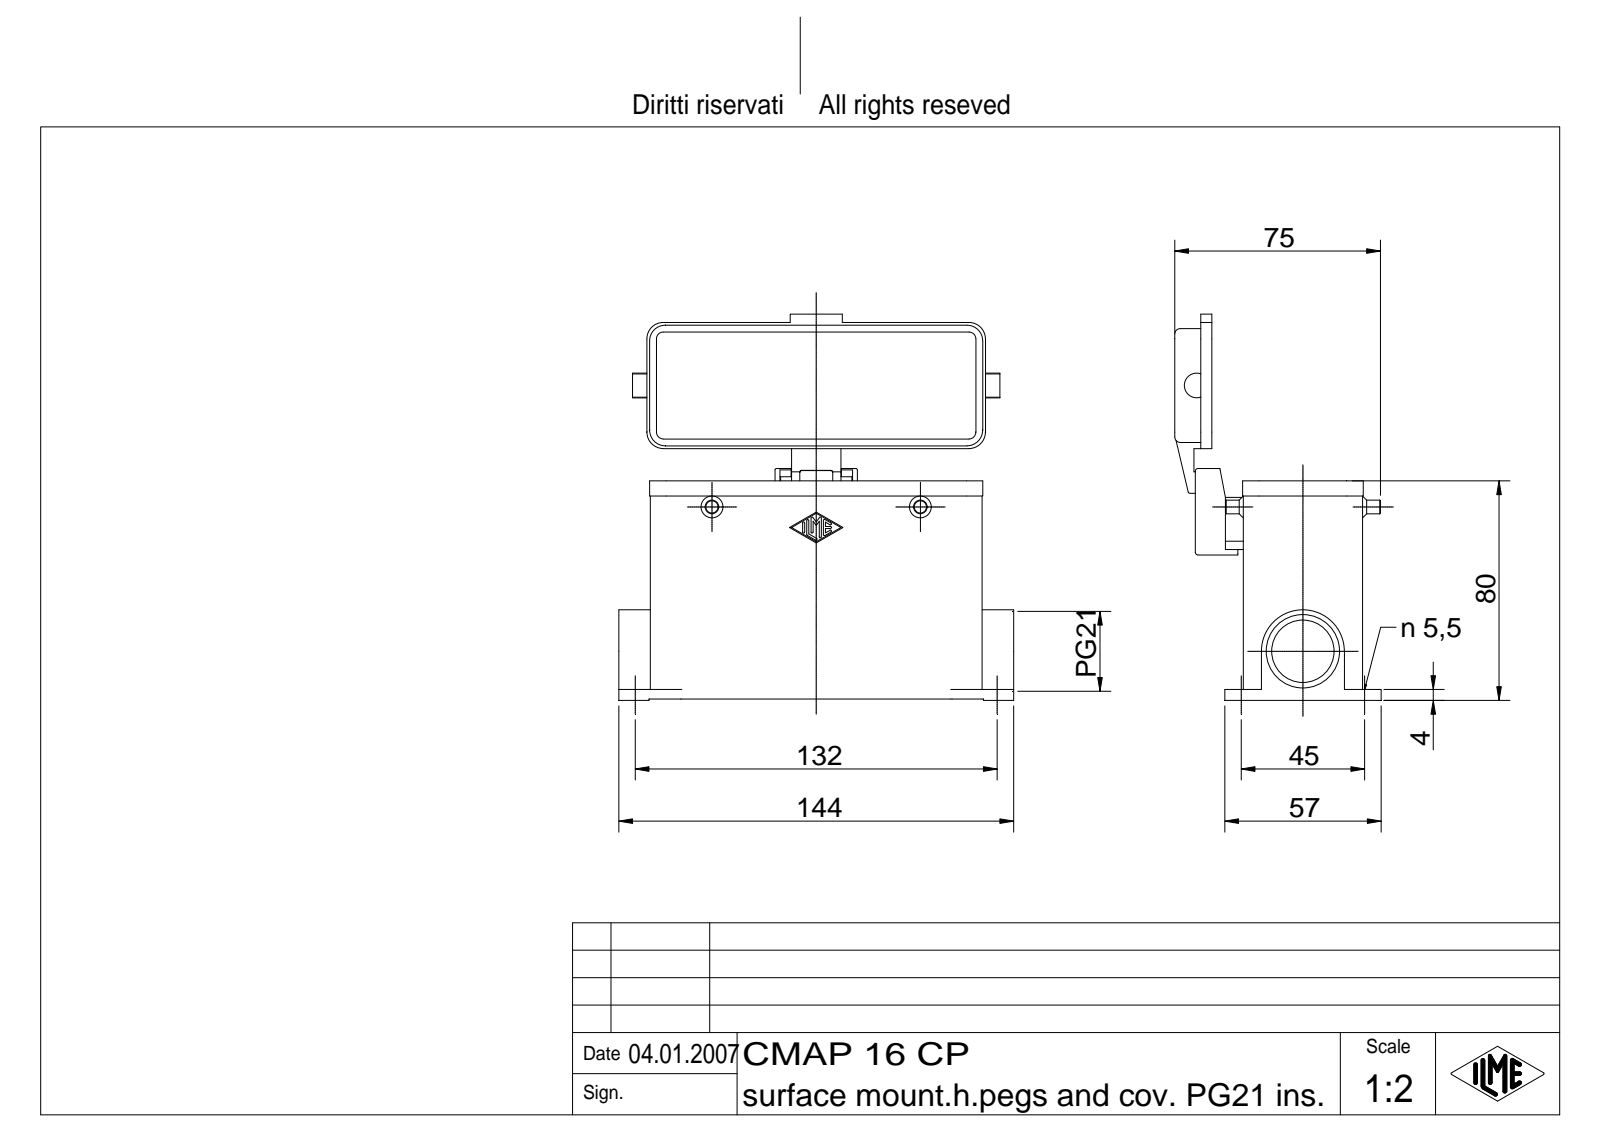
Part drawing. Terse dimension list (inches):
name: CMAP 16 CP
written by: Autodesk Inventor 7 (AUTOMOTIVE_DESIGN)
unit: in
bodies: 1 solid, 470 faces (195 planar, 164 cylindrical, 111 other)
size: 5.669 × 5.541 × 2.963
volume: 9.396 in³; area: 140.6 in²
holes: 4× ⌀0.217, 1× ⌀0.157, 1× ⌀0.197, 1× ⌀0.897, 1× ⌀1.054
bosses: 2× ⌀0.197, 2× ⌀0.118, 1× ⌀0.276, 1× ⌀0.157
rounds: 14× R0.015, 14× R0.039, 12× R0.236, 10× R0.02, 8× R0.028, 8× R0.079, 4× R0.098, 4× R0.118
face distances: 0.118, 1.594, 1.713, 1.476, 0.098, 0.138, 0.886, 2.48, 2.697, 2.598
hole spacings: 1.772, 5.197, 5.491
